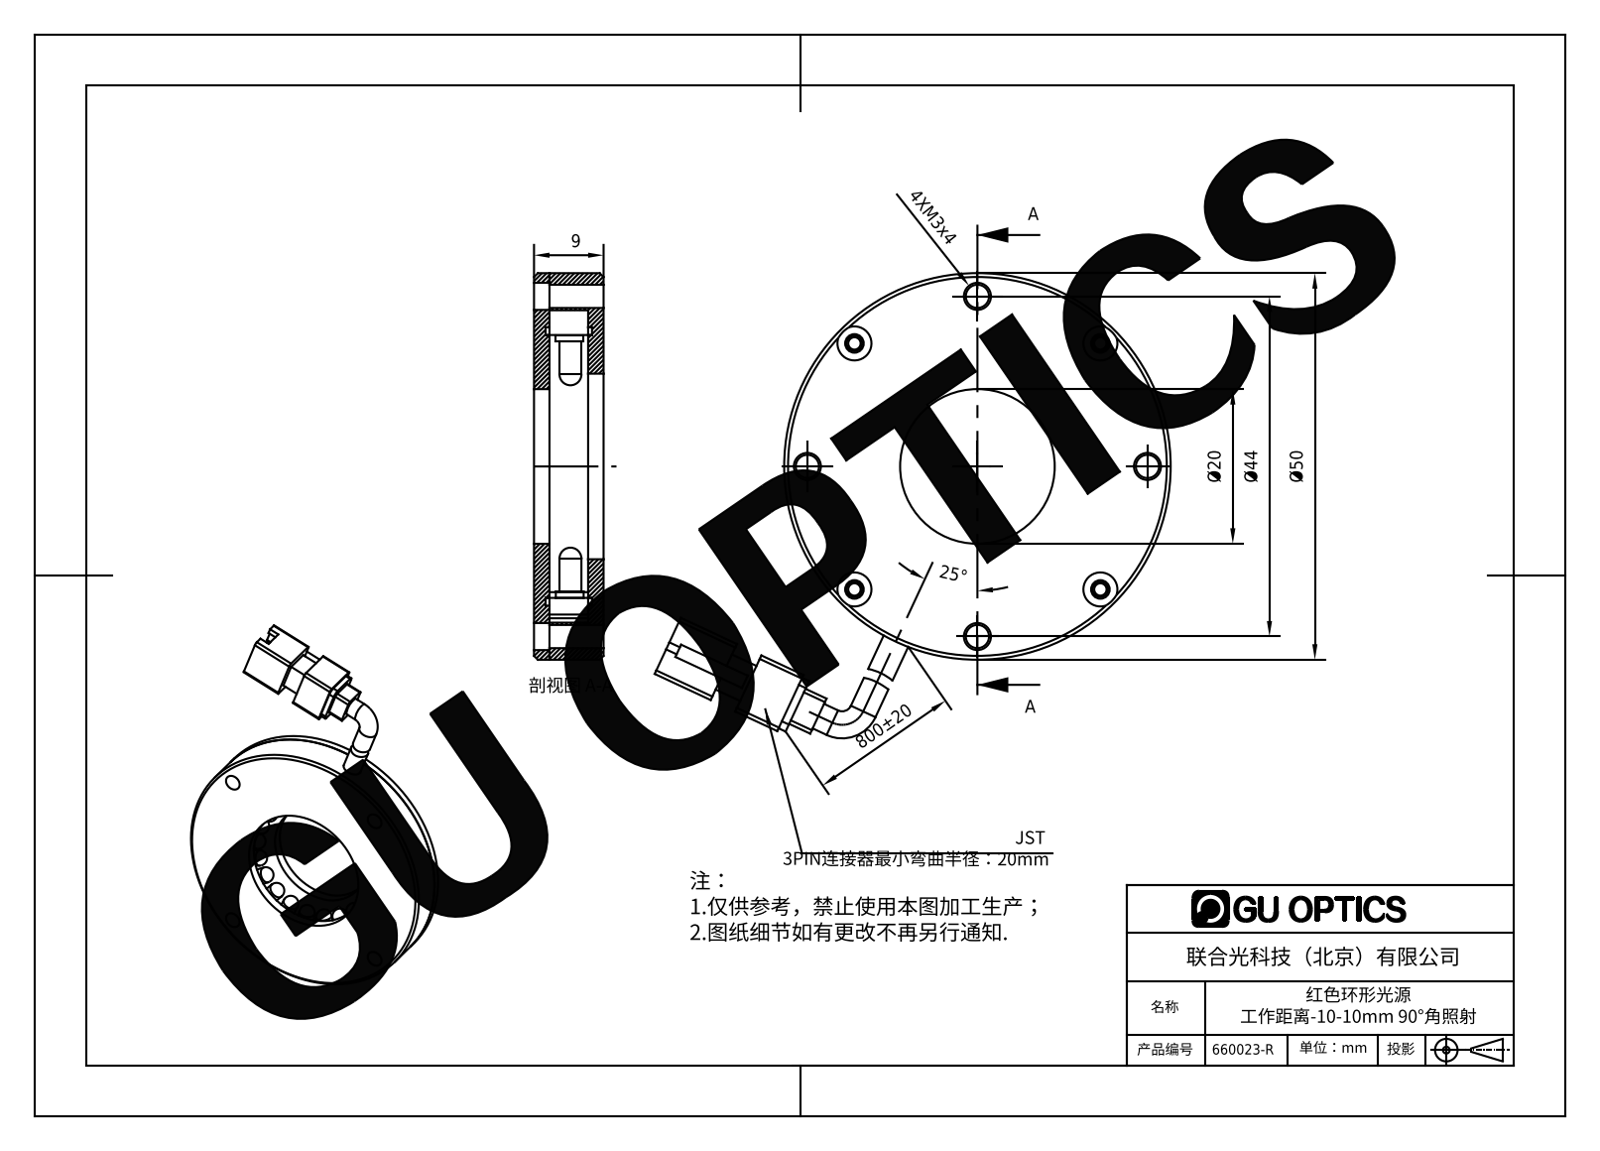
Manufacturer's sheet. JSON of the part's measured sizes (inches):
{"part_name": "660023-R", "step_written_by": "SolidWorks 2016 (AUTOMOTIVE_DESIGN)", "units": "inches", "bodies": {"solids": 26, "faces": 561, "planar": 329, "cylindrical": 187, "other": 45}, "overall_size": [2.894, 1.969, 0.394], "volume_in3": 0.687, "surface_area_in2": 20.77, "round_holes": [[0.118, 5], [0.138, 5], [0.063, 4], [0.079, 4], [0.094, 4], [0.787, 1], [0.945, 1], [1.417, 1], [1.591, 1]], "round_bosses_or_shafts": [[0.15, 21], [0.118, 21], [0.138, 2], [1.969, 1], [1.354, 1], [1.339, 1]], "partial_cylinders_radius": [[0.02, 12], [0.039, 4]], "face_to_face_distances": [0.276, 0.079, 0.354, 0.197, 0.02, 0.039, 0.217, 0.059, 0.236, 0.295], "hole_center_spacings": [0.671, 0.886, 1.253, 1.619, 1.619, 0.67, 0.866, 0.867]}
